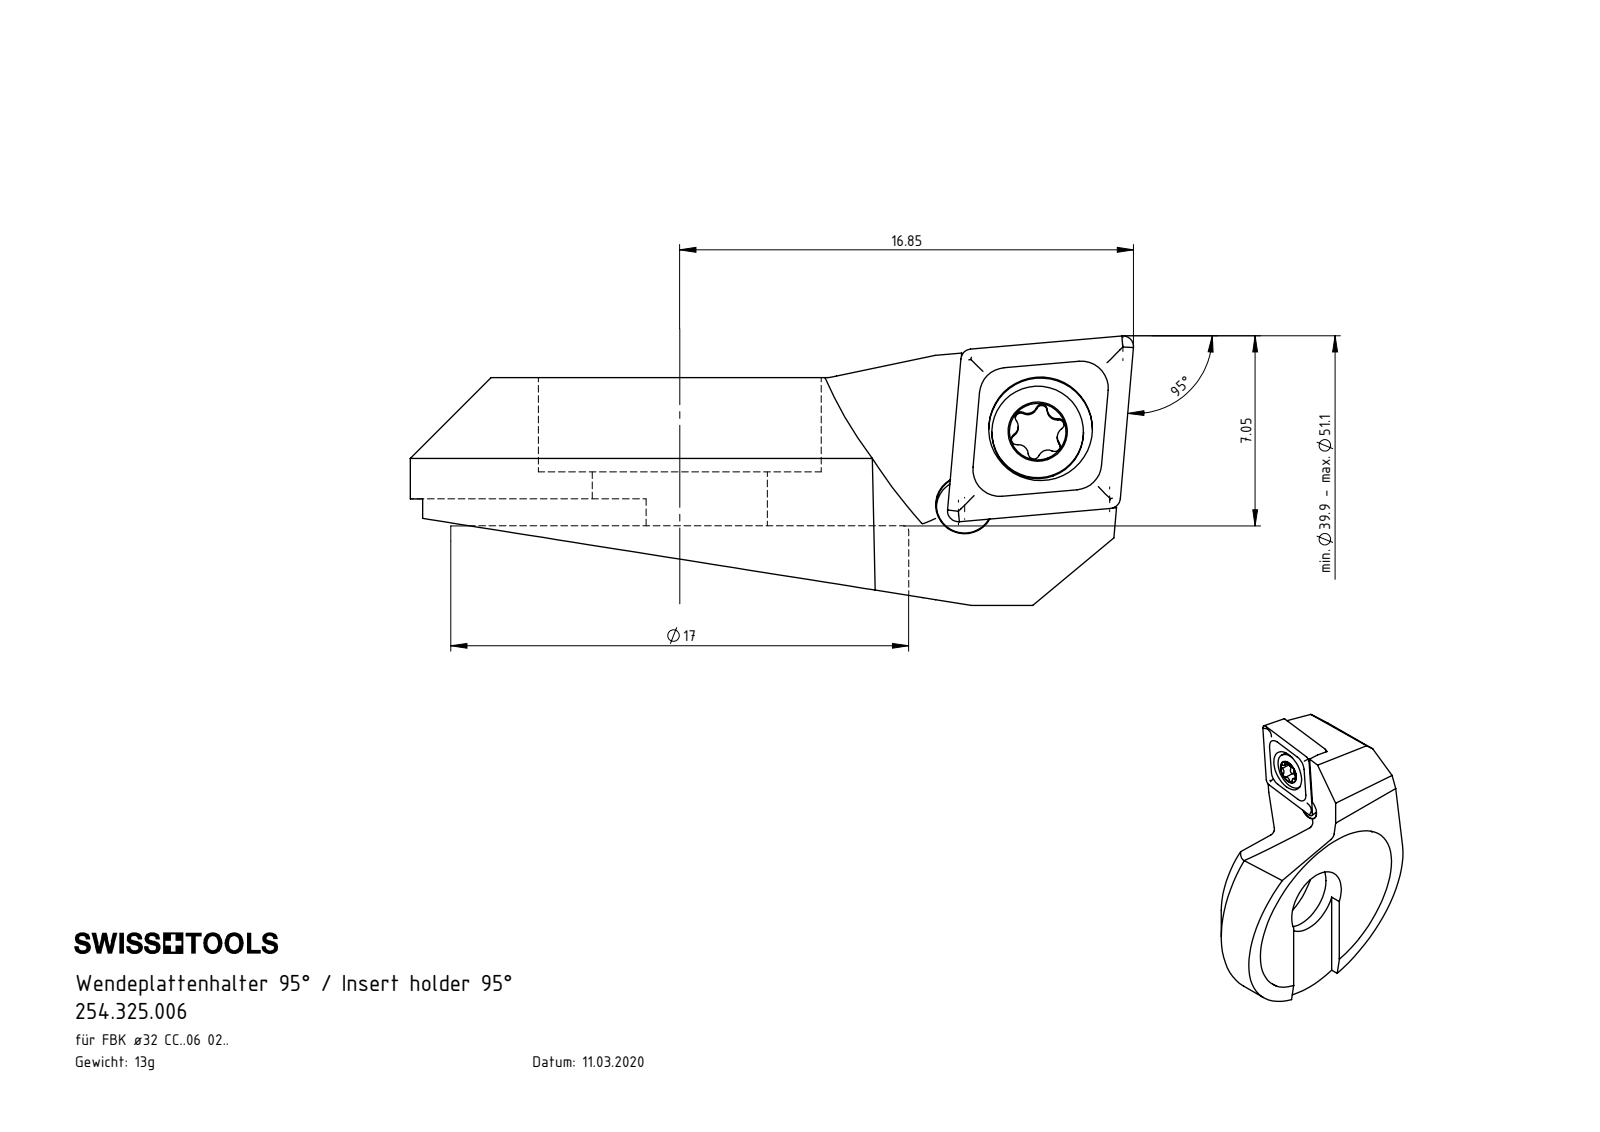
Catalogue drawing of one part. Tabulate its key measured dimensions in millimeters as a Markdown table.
| quantity | value |
| --- | --- |
| part name | 254.325.006; WCA-ER2.001.006_A; CCMT060204; F32-WCA.002.007_A_fertigbearbeitet |
| STEP written by | SolidWorks 2017 (CONFIG_CONTROL_DESIGN) |
| units | millimeters |
| bodies | 3 solids, 135 faces (40 planar, 45 cylindrical, 50 other) |
| overall size | 26.85 × 20 × 10 |
| volume | 1 584 mm³ |
| surface area | 1 546 mm² |
| round holes (diameter × count) | 2 × 1, 2.05 × 1, 2.8 × 1, 3.85 × 1, 6.5 × 1, 10.5 × 1 |
| round bosses / shafts (diameter × count) | 3.4 × 1, 2.5 × 1 |
| partial cylindrical surfaces (radius × count) | 0.21 × 6, 0.36 × 5, 1 × 4, 0.36 × 1, 4 × 1, 8.5 × 1, 10 × 1, 12 × 1 |
| main face-to-face distances | 1, 2, 4.95, 3.95, 2.95, 2.28, 2.38, 6, 2.68, 2.58 |
| hole center spacings | 3.91, 4.01 |
